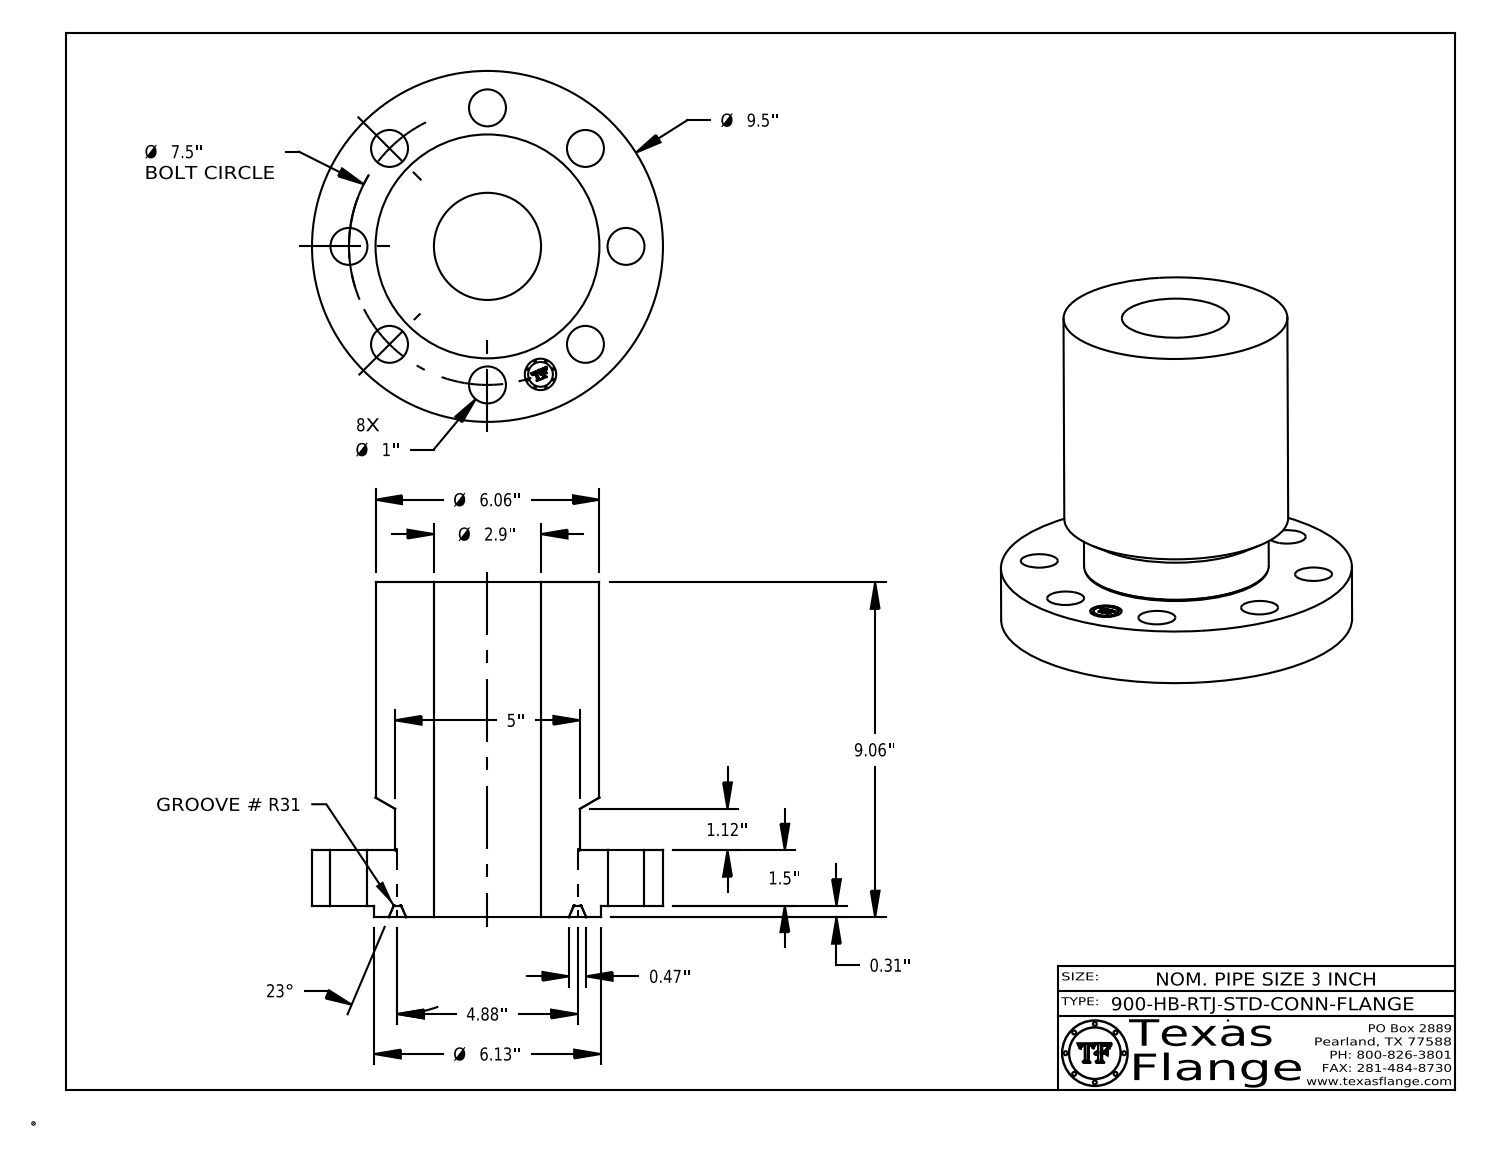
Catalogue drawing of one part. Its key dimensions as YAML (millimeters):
part_name: "3-900-HB-RTJ-STD-CONN-FLANGE"
step_written_by: "CATIA V5 STEP AP214 (AUTOMOTIVE_DESIGN)"
units: millimeters
bodies: {solids: 1, faces: 431, planar: 371, cylindrical: 46, other: 14}
overall_size: [241.3, 241.3, 230.2]
volume: 3966000
surface_area: 285300
round_holes:
  - {diameter: 25.4, count: 8}
  - {diameter: 21.6, count: 1}
  - {diameter: 73.7, count: 1}
round_bosses_or_shafts:
  - {diameter: 1.3, count: 8}
  - {diameter: 241.3, count: 1}
  - {diameter: 155.6, count: 1}
  - {diameter: 153.9, count: 1}
  - {diameter: 127, count: 1}
  - {diameter: 17, count: 1}
face_to_face_distances: [38.1, 222.3, 184.2, 8, 46.1, 230.2, 45.9, 38, 184.3, 6.5]
hole_center_spacings: [95.3, 72.9, 134.7, 176, 37.2, 158.4, 186.8, 190.5]
